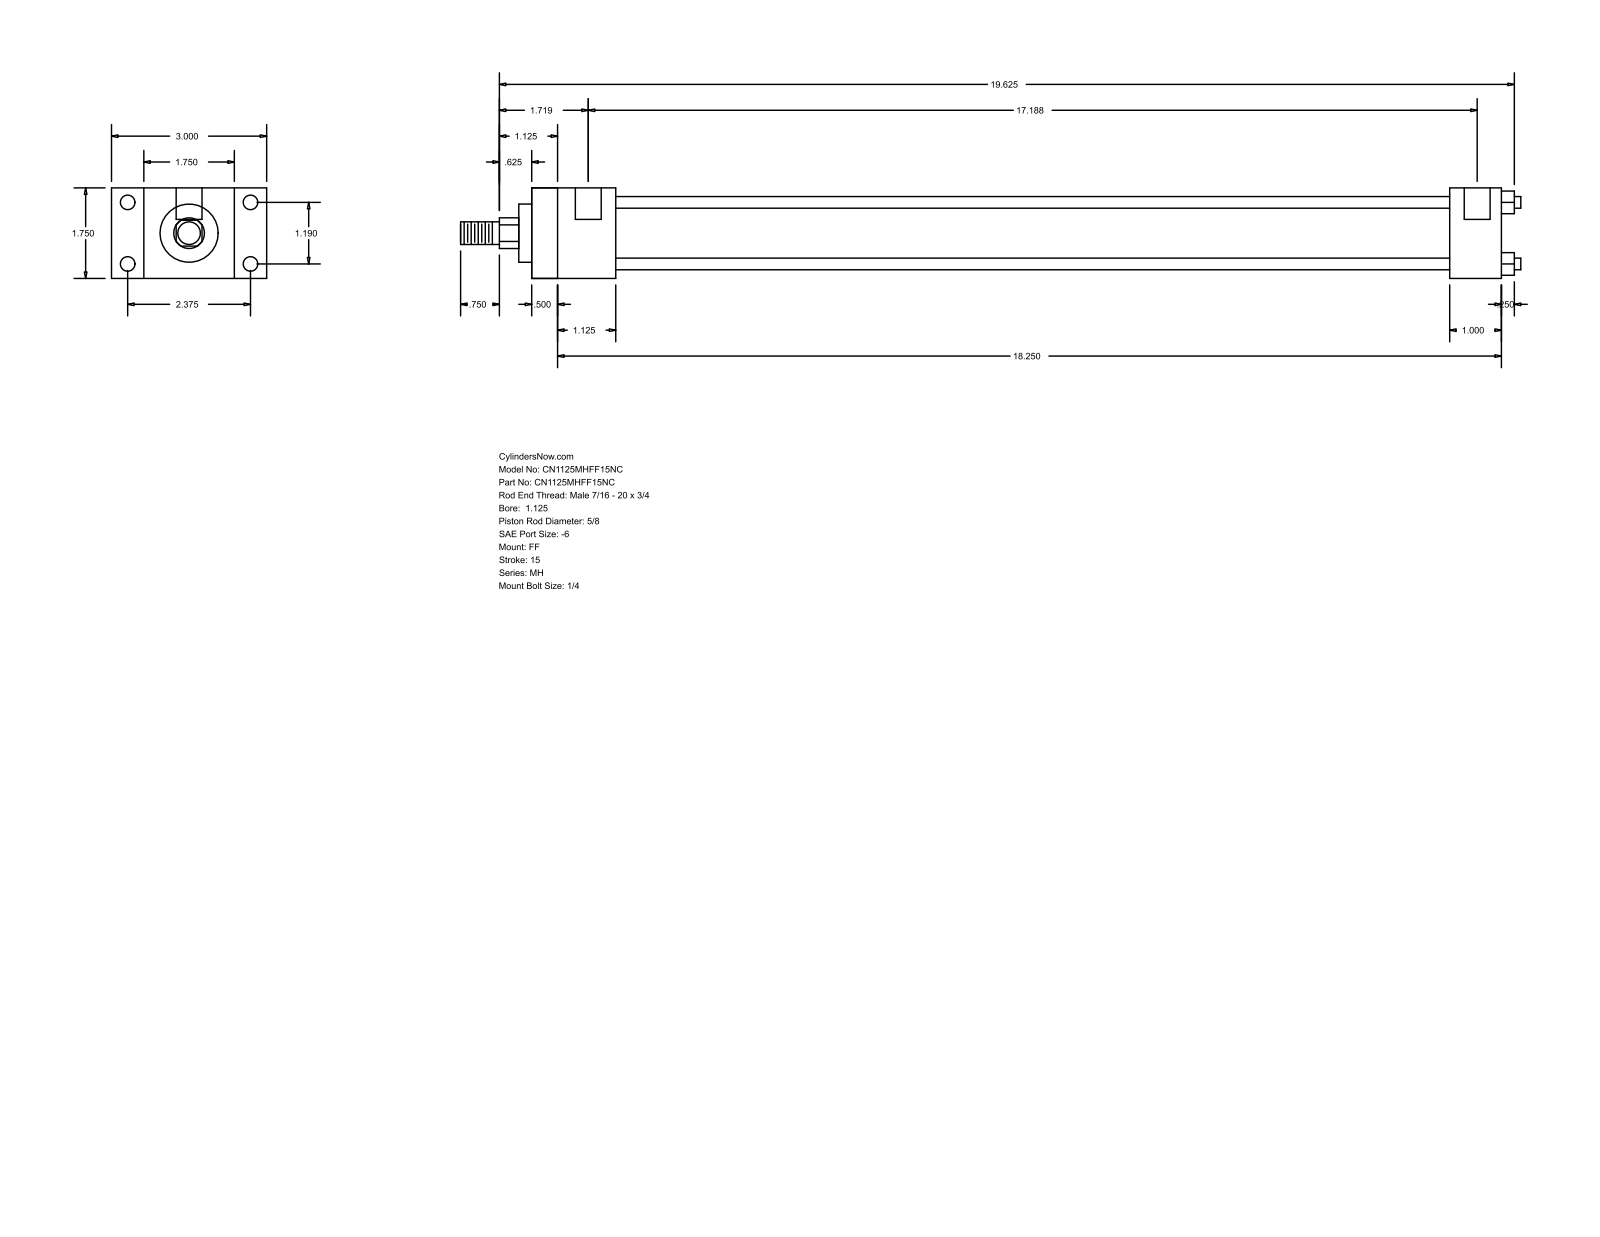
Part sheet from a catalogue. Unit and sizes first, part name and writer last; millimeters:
Units: millimetres
Overall size (bounding box): 520.7 × 76.2 × 44.45
Round holes (diameter × count): ⌀5.56 ×4, ⌀7.14 ×4, ⌀12.7 ×2
Round bosses / shafts (diameter × count): ⌀5.71 ×4, ⌀34.92 ×1, ⌀28.57 ×1, ⌀15.88 ×1, ⌀11.11 ×1
Partial cylindrical surfaces — rounded edges, fillets, slot ends (radius × count): R7.54 ×1
Main face-to-face distances: 44.46, 476.24, 15.87, 12.69, 463.55, 28.58, 60.33, 41.27, 450.85, 438.16
Hole centre spacings: 30.22, 60.32, 67.47, 433.39, 3.17, 436.56
Bodies: 0 solids, 92 faces (64 planar, 28 cylindrical, 0 other)
Part name (STEP PRODUCT): MH_FF__0112_0.625
STEP written by: GSSL Pune (CONFIG_CONTROL_DESIGN)
